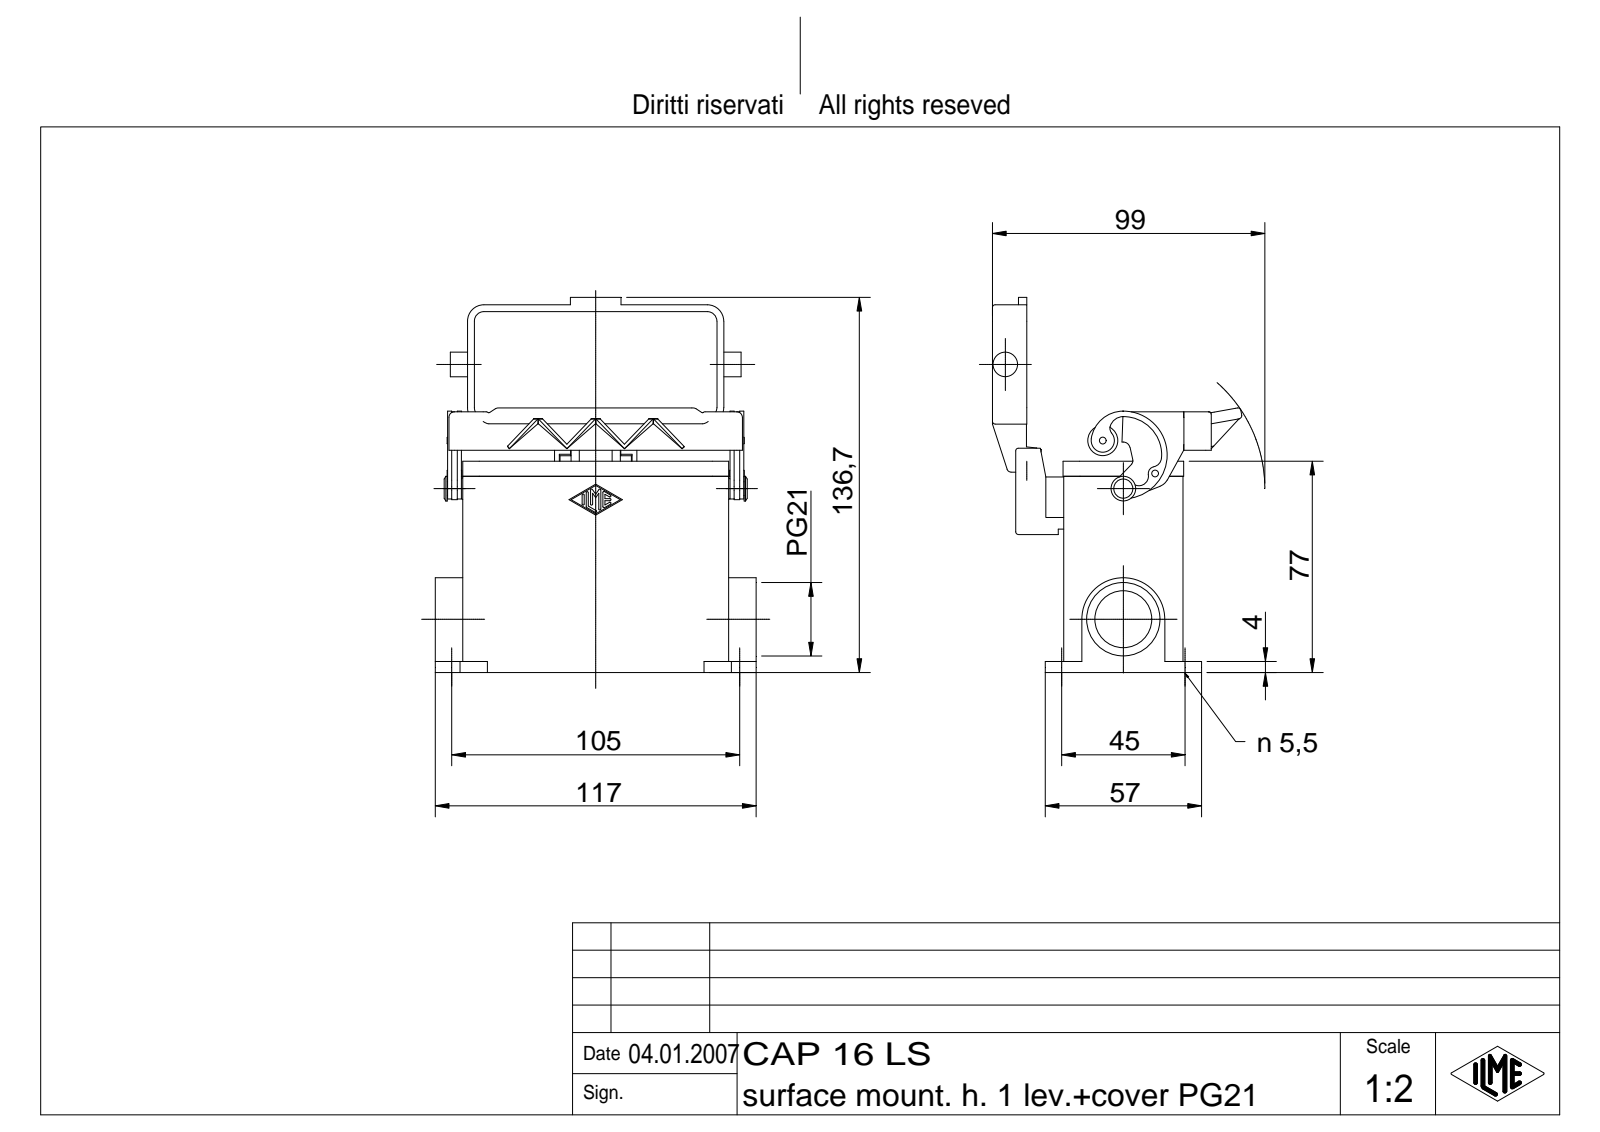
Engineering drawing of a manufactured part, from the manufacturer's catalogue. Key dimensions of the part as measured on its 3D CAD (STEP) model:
Part name (STEP PRODUCT): CAP_16_LS
STEP written by: Creo Elements/Direct Modeling 20.1B 02-Apr-2019 (C) Parametric Technology GmbH (AUTOMOTIVE_DESIGN)
Units: millimetres
Bodies: 1 solid, 573 faces (274 planar, 211 cylindrical, 88 other)
Overall size (bounding box): 137.99 × 117 × 91.12
Volume: 164 917 mm³ · Surface area: 86 303 mm²
Round holes (diameter × count): ⌀2.6 ×4, ⌀3.5 ×4, ⌀24.5 ×1, ⌀27 ×1, ⌀32 ×1, ⌀35.7 ×1
Round bosses / shafts (diameter × count): ⌀43.87 ×1, ⌀11 ×1, ⌀9 ×1, ⌀8 ×1, ⌀4.8 ×1, ⌀3.2 ×1
Partial cylindrical surfaces — rounded edges, fillets, slot ends (radius × count): R1 ×30, R3 ×23, R2 ×13, R7 ×9, R1.5 ×5, R1.8 ×4, R4.2 ×4, R0.1 ×3
Main face-to-face distances: 35.5, 2, 62.6, 27.1, 4, 64.6, 29.1, 3, 14.25, 3.5
Hole centre spacings: 27, 77.5, 82.07
